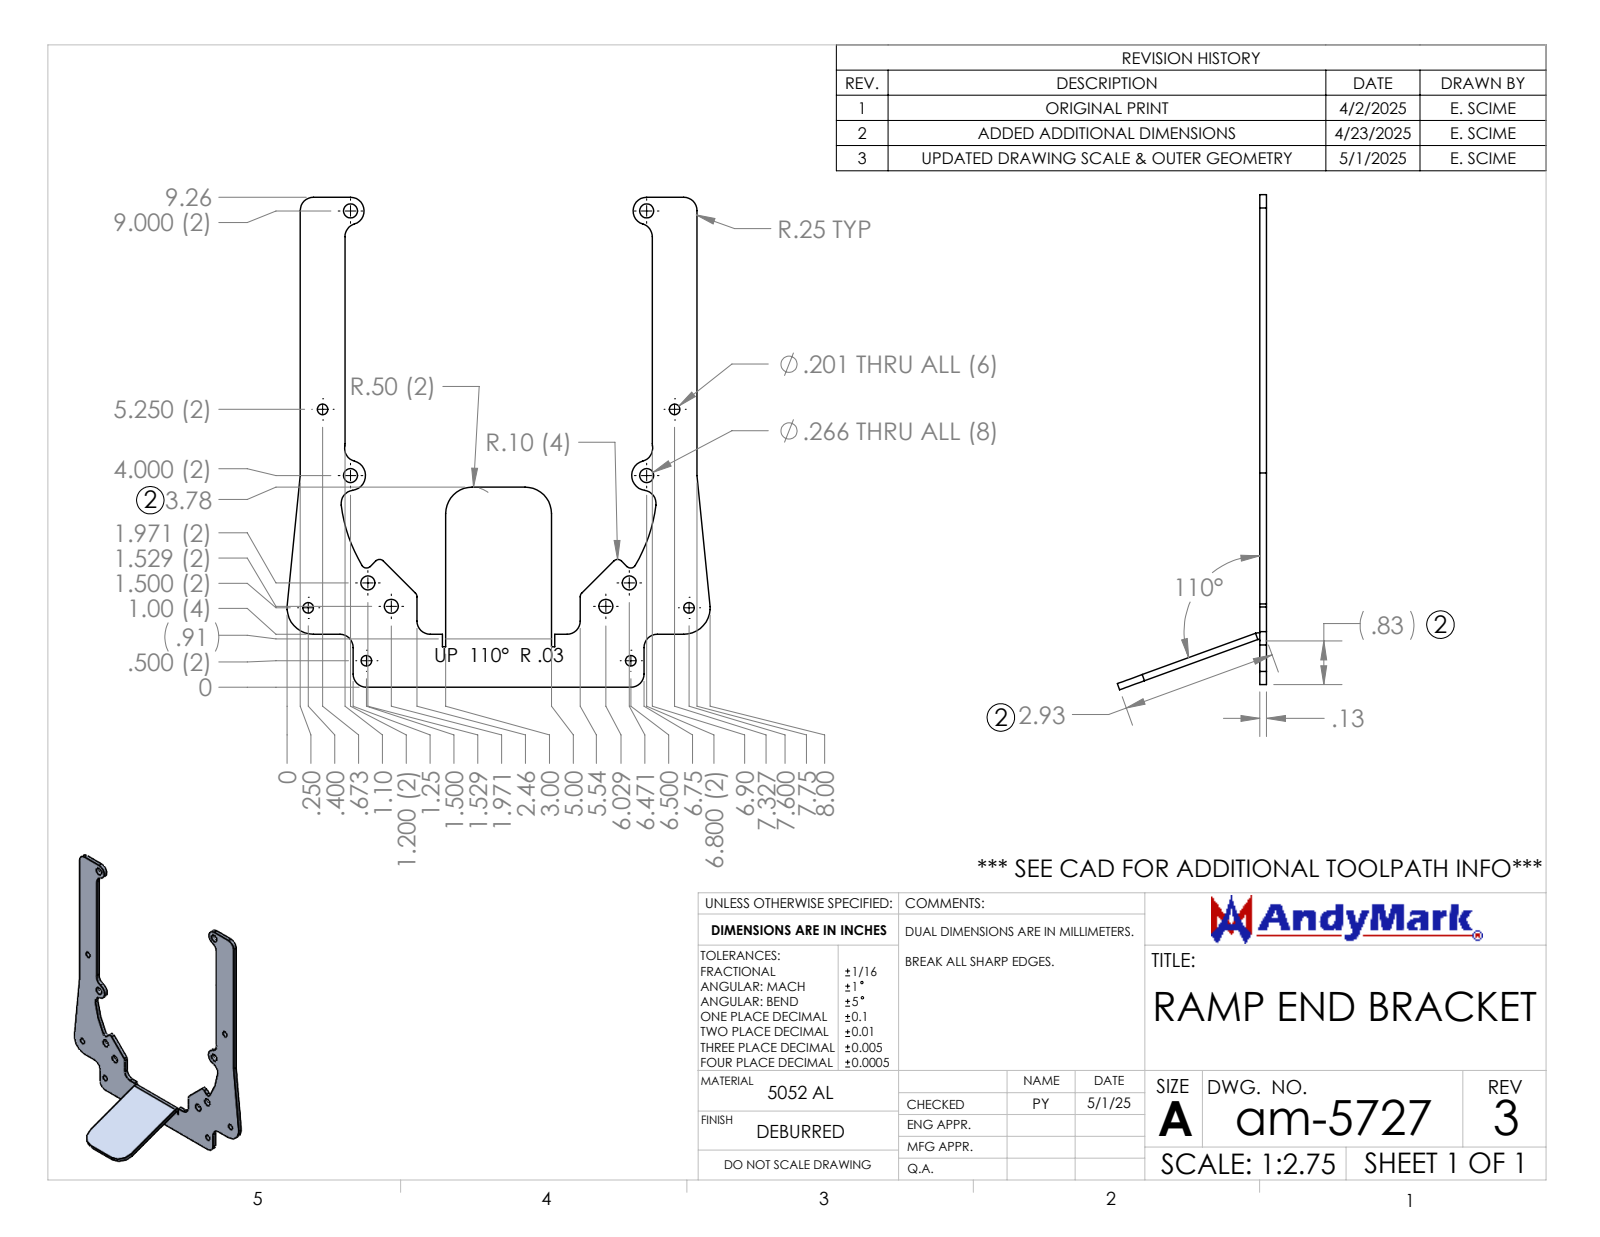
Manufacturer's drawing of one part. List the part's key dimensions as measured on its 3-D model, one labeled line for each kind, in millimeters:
Part name (STEP PRODUCT): am-5727 Ramp End Bracket
STEP written by: SolidWorks 2024 (AUTOMOTIVE_DESIGN)
Units: millimetres
Bodies: 1 solid, 105 faces (36 planar, 69 cylindrical, 0 other)
Overall size (bounding box): 237.6 × 203.2 × 71.6
Volume: 59 800 mm³ · Surface area: 43 030 mm²
Round holes (diameter × count): ⌀6.8 ×8, ⌀5.1 ×6
Partial cylindrical surfaces — rounded edges, fillets, slot ends (radius × count): R6.4 ×18, R2.5 ×6, R6.6 ×2, R7.2 ×2, R12.7 ×2, R12.7 ×2, R0.7 ×1, R3.9 ×1
Main face-to-face distances: 3.2, 3.2, 21.5, 169, 69.9, 120.7, 48.4, 99.2, 190.5, 147.5
Hole centre spacings: 127, 15.9, 28.7, 34.5, 37.4, 37.8, 52.2, 66.7
